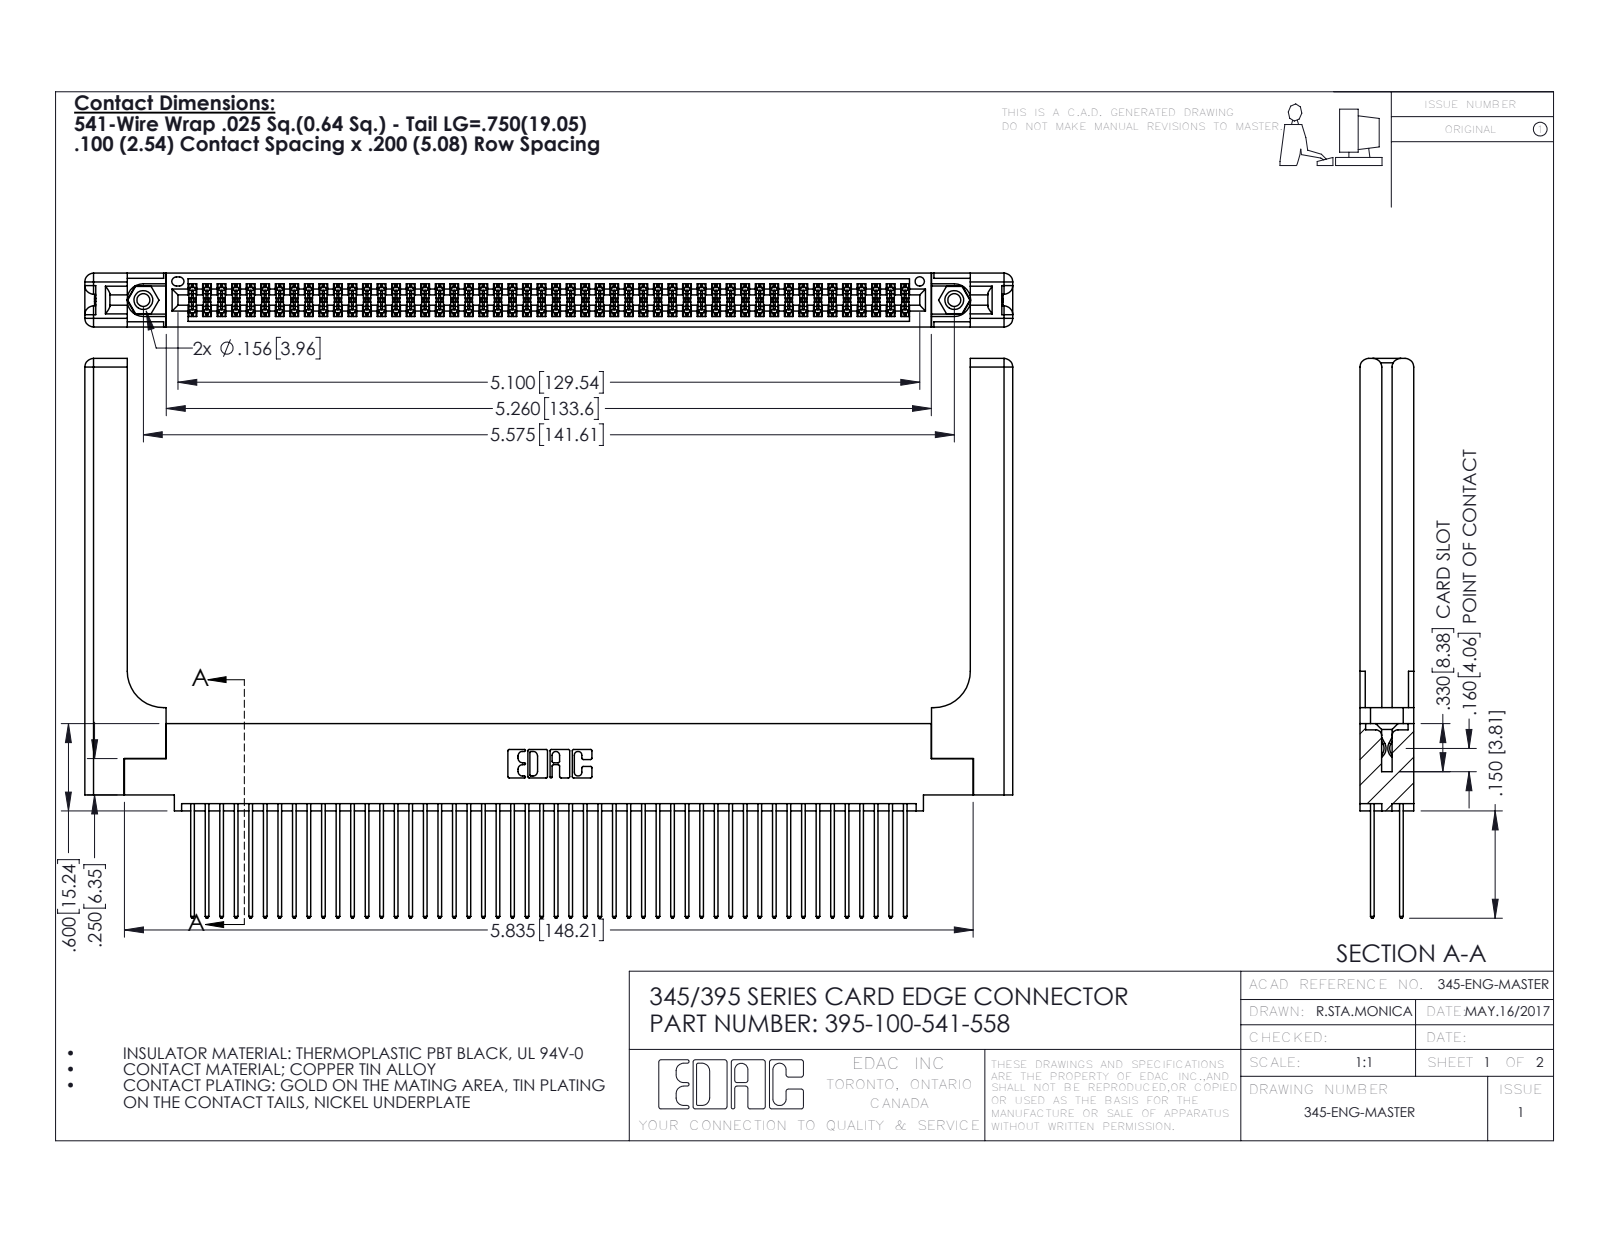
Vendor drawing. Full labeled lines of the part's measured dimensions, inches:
Part name (STEP PRODUCT): 395-100-541-558; 345-292-001_345-293-141; 345 Part_0.110 Offset - 0.156 Dia-TH; 345-220-058_345-220-058 (+1 more)
STEP written by: SolidWorks 2016 (CONFIG_CONTROL_DESIGN)
Units: inches
Bodies: 105 solids, 5386 faces (3532 planar, 1794 cylindrical, 60 other)
Overall size (bounding box): 6.379 × 3.847 × 0.37
Volume: 1.513 in³ · Surface area: 49.78 in²
Round holes (diameter × count): ⌀0.089 ×2, ⌀0.125 ×2, ⌀0.156 ×2, ⌀0.064 ×1
Round bosses / shafts (diameter × count): ⌀0.155 ×2
Partial cylindrical surfaces — rounded edges, fillets, slot ends (radius × count): R0.006 ×150, R0.01 ×100, R0.01 ×22, R0.06 ×16, R0.007 ×6, R0.031 ×6, R0.026 ×3, R0.014 ×2
Main face-to-face distances: 0.072, 0.298, 0.37, 0.098, 0.272, 0.025, 0.2, 0.225, 0.175, 0.148
Hole centre spacings: 0.27, 5.339, 5.575
